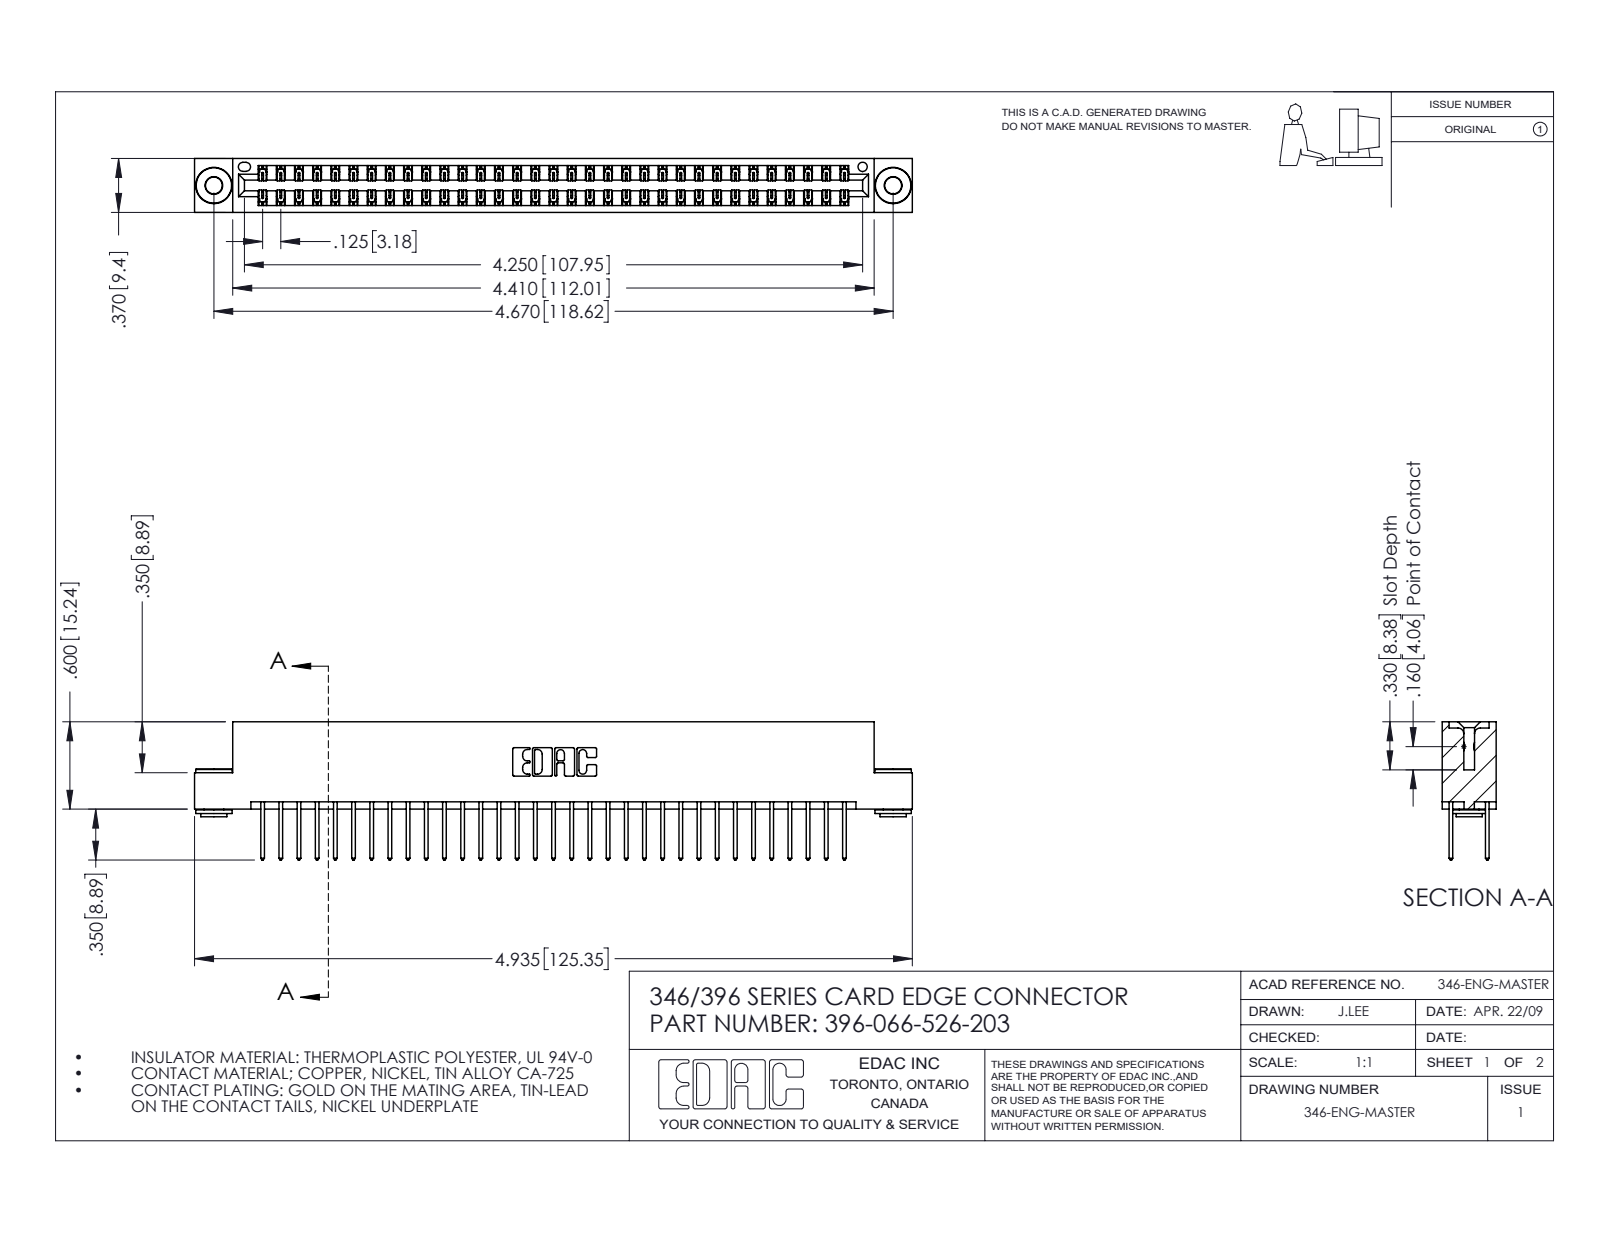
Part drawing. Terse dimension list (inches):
name: 346 Part_Flush Mounting Lugs - 0.156 Dia-TH; 396-066-526-203; 345-250-002_345-250-002-102; 345-292-001_345-293-126
written by: SolidWorks 2016 (CONFIG_CONTROL_DESIGN)
unit: in
bodies: 69 solids, 3592 faces (2396 planar, 1188 cylindrical, 8 other)
size: 4.935 × 0.95 × 0.37
volume: 0.749 in³; area: 27.03 in²
holes: 2× ⌀0.116, 2× ⌀0.156, 1× ⌀0.064
bosses: 2× ⌀0.25, 2× ⌀0.18, 2× ⌀0.136
rounds: 99× R0.006, 66× R0.01, 22× R0.01, 6× R0.007, 6× R0.031, 3× R0.026, 2× R0.014, 2× R0.022
face distances: 0.048, 0.322, 0.25, 0.37, 0.025, 0.072, 0.298, 0.275, 0.148, 0.222
hole spacings: 0.246, 4.462, 4.67
